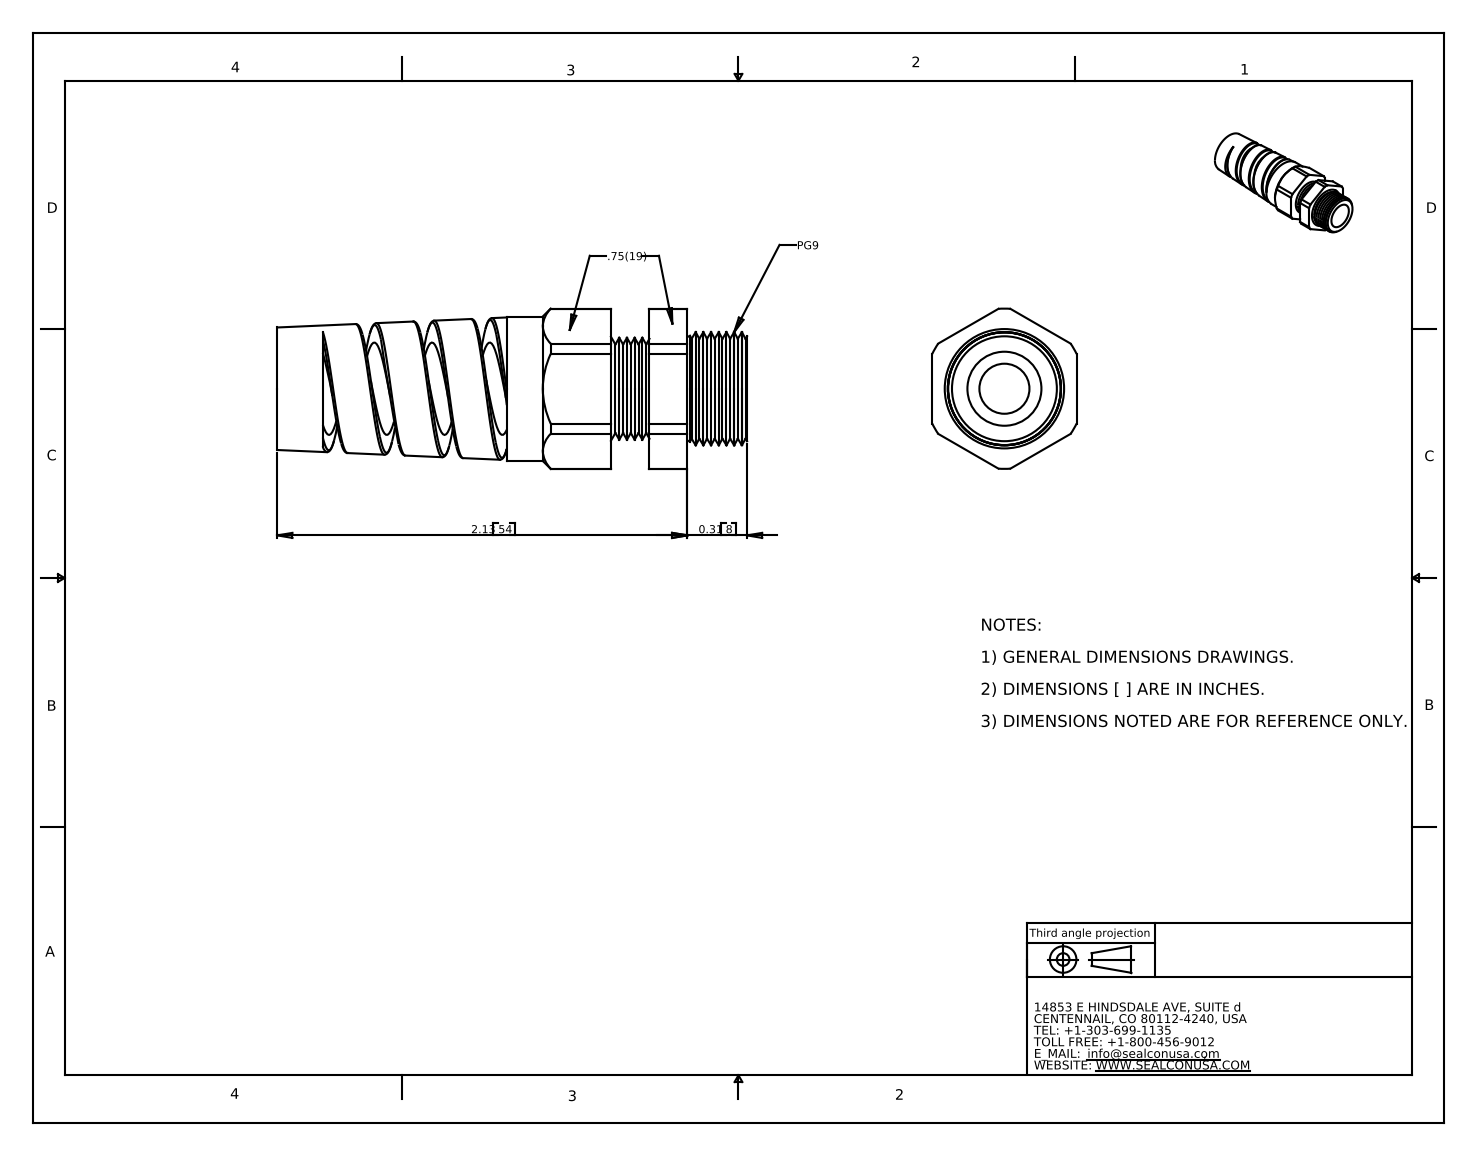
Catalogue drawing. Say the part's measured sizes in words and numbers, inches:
The part is named "CF09BA-GY". Its 3-D file was written by "SolidWorks 2007 (CONFIG_CONTROL_DESIGN)". It is 2 solids with 140 faces: 24 planar, 31 cylindrical and 85 other. Overall it measures 2.44 by 0.833 by 0.75 inches. Its volume is 0.532 cubic inches and its surface area 12.16 square inches. Round holes: 1 of diameter 0.26, 1 of diameter 0.48, 1 of diameter 0.54. Round bosses or shafts: 1 of diameter 0.75. Partial cylindrical surfaces (rounded edges, fillets, slot ends): 1 of radius 0.25, 1 of radius 0.416. The main face-to-face distances are 0.75, 0.2, 0.75, 0.397, 0.197, 1.733, 1.933, 2.13, 2.44, 0.707.
